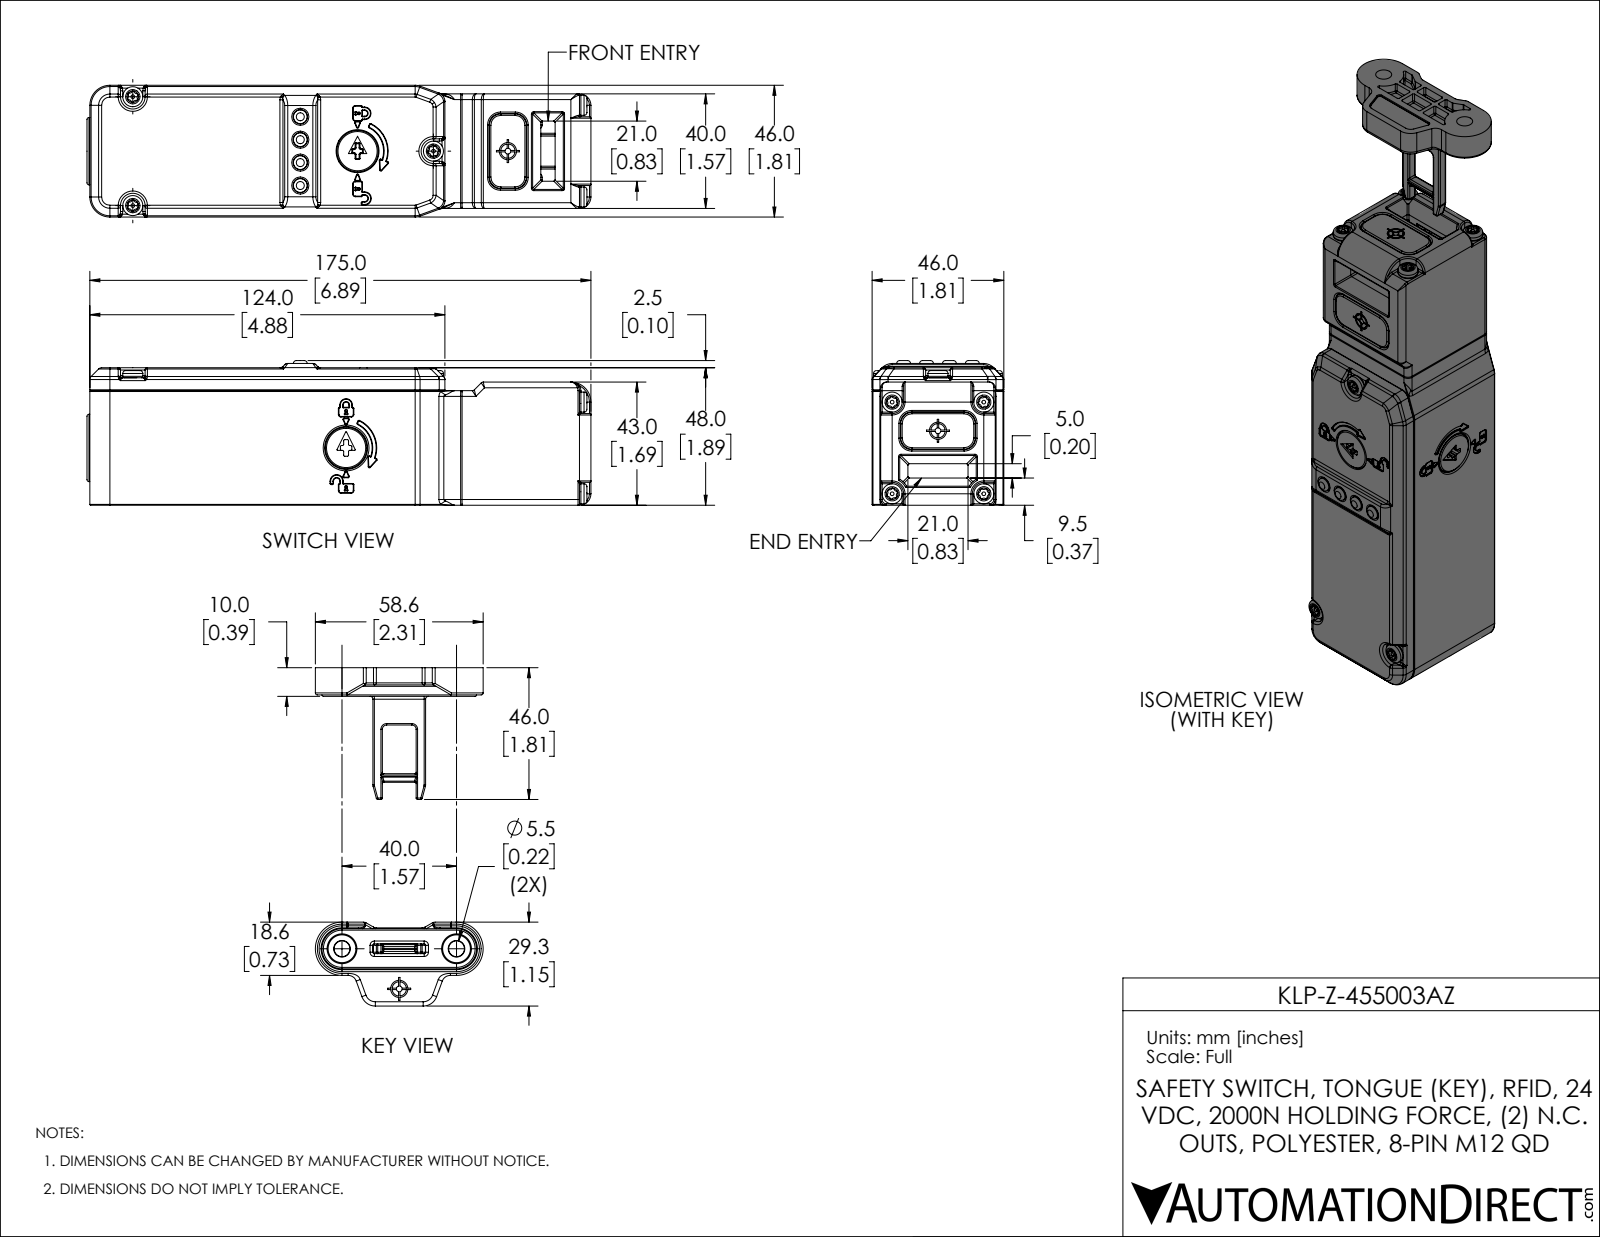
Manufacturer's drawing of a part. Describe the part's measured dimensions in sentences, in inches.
The part is named "455-KLP-Z-AZ". Its 3-D file was written by "SolidWorks 2019 (AUTOMOTIVE_DESIGN)". It is 23 solids with 3910 faces: 1161 planar, 1576 cylindrical and 1173 other. Overall it measures 8.937 by 2.307 by 1.988 inches. Its volume is 18.03 cubic inches and its surface area 140.7 square inches. Round holes: 13 of diameter 0.157, 6 of diameter 0.094, 6 of diameter 0.197, 6 of diameter 0.236, 4 of diameter 0.177, 4 of diameter 0.366, 3 of diameter 0.142, 3 of diameter 0.169, 3 of diameter 0.217, 2 of diameter 0.13, 2 of diameter 0.22, 2 of diameter 0.591. Round bosses or shafts: 11 of diameter 0.138, 7 of diameter 0.276, 7 of diameter 0.051, 6 of diameter 0.189, 4 of diameter 0.039, 3 of diameter 0.197, 2 of diameter 0.571, 2 of diameter 0.307. Partial cylindrical surfaces (rounded edges, fillets, slot ends): 511 of radius 0.02, 164 of radius 0.012, 124 of radius 0.008, 122 of radius 0.039, 44 of radius 0.079, 27 of radius 0.059, 25 of radius 0.157, 20 of radius 0.028. The main face-to-face distances are 1.575, 0.118, 1.811, 1.693, 0.315, 0.039, 1.89, 0.098, 1.449, 0.138. The hole center spacings are 0.319, 0.481, 0.63, 0.748, 0.891, 1.043, 1.043, 1.081.
